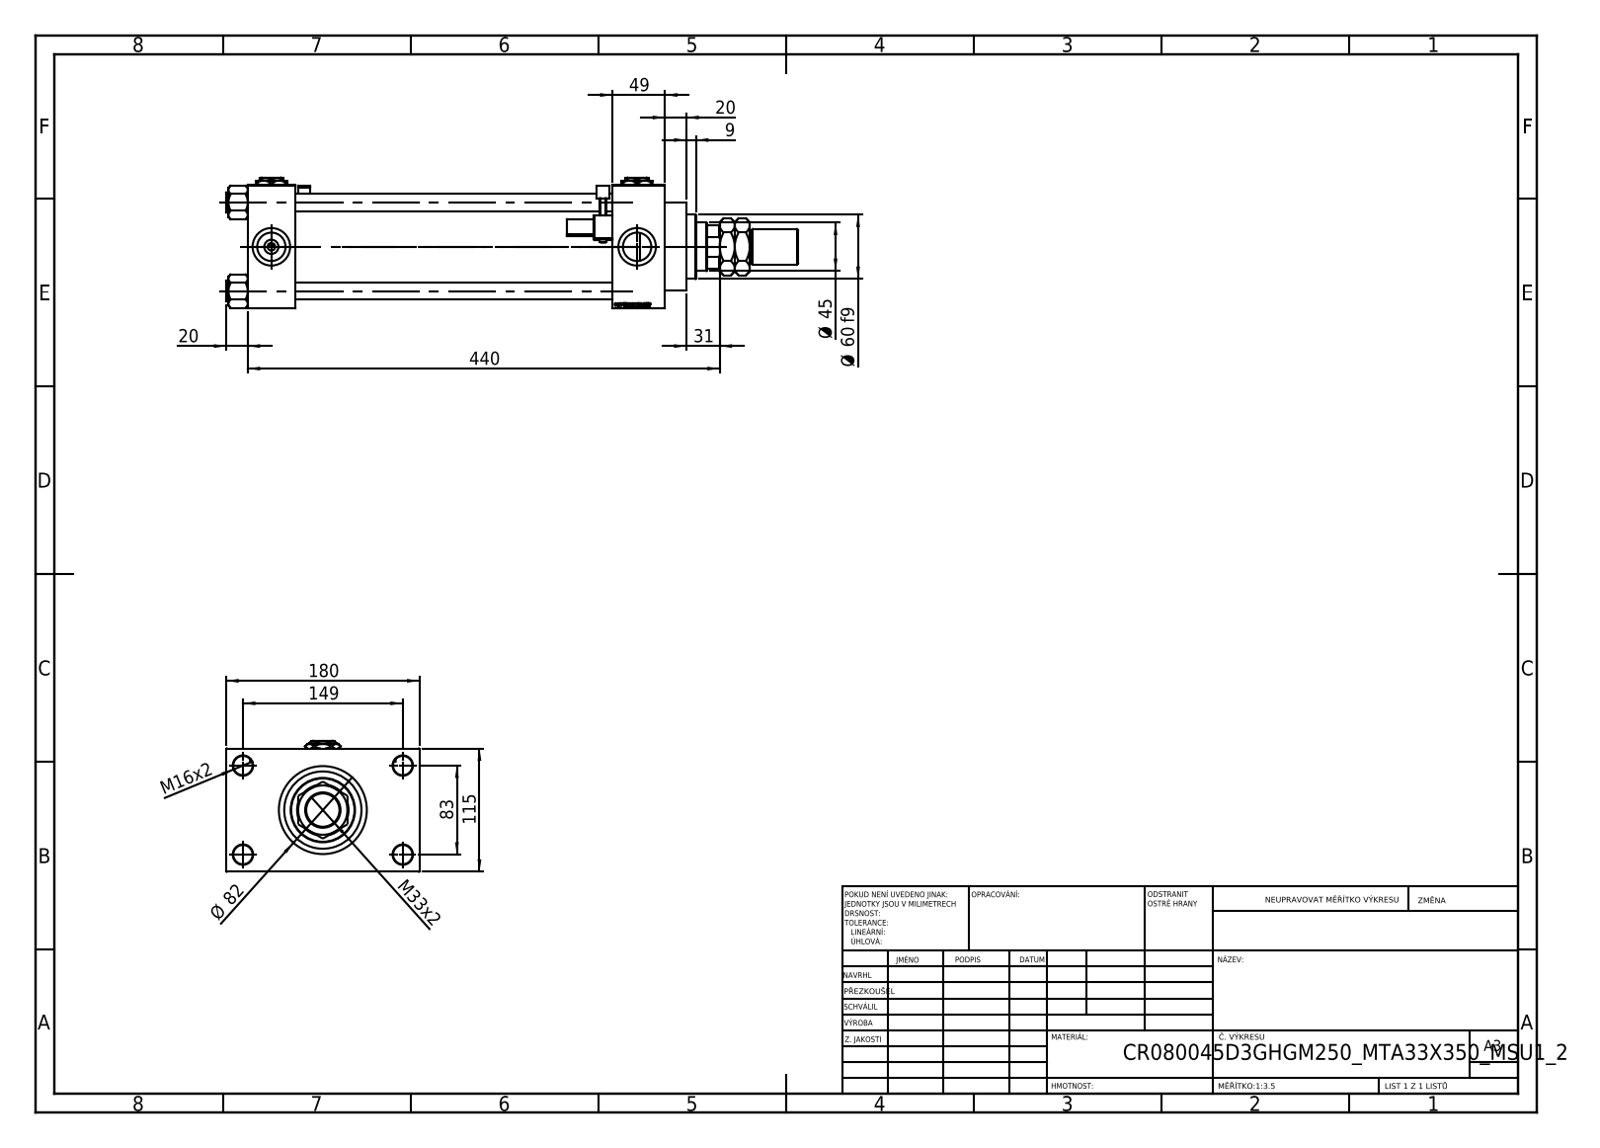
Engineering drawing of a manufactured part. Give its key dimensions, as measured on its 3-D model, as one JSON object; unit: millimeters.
{"part_name": "NUT_M5_D; V215CR_VCP_D; V215CR_D_Body; MTA (+4 more)", "step_written_by": "SolidWorks 2019 (CONFIG_CONTROL_DESIGN)", "units": "millimeters", "bodies": {"solids": 16, "faces": 1455, "planar": 666, "cylindrical": 163, "other": 626}, "overall_size": [533, 180, 122], "volume_mm3": 2851000, "surface_area_mm2": 532978, "round_holes": [[16, 4], [18, 4], [26.44, 4], [35, 4], [7, 3], [31.5, 1], [45, 1], [48, 1], [61, 1], [72, 1], [80, 1]], "round_bosses_or_shafts": [[19, 4], [6, 2], [86, 1], [82, 1], [60, 1], [33, 1], [31, 1]], "partial_cylinders_radius": [[0.5, 48], [1, 2], [2.5, 2], [4, 2], [22, 1]], "face_to_face_distances": [115, 296, 345, 49, 44, 340, 389, 32.5, 147.5, 46], "hole_center_spacings": [33.15, 58.48, 82.7, 85.28, 89.24, 115.85, 142.43, 83]}
